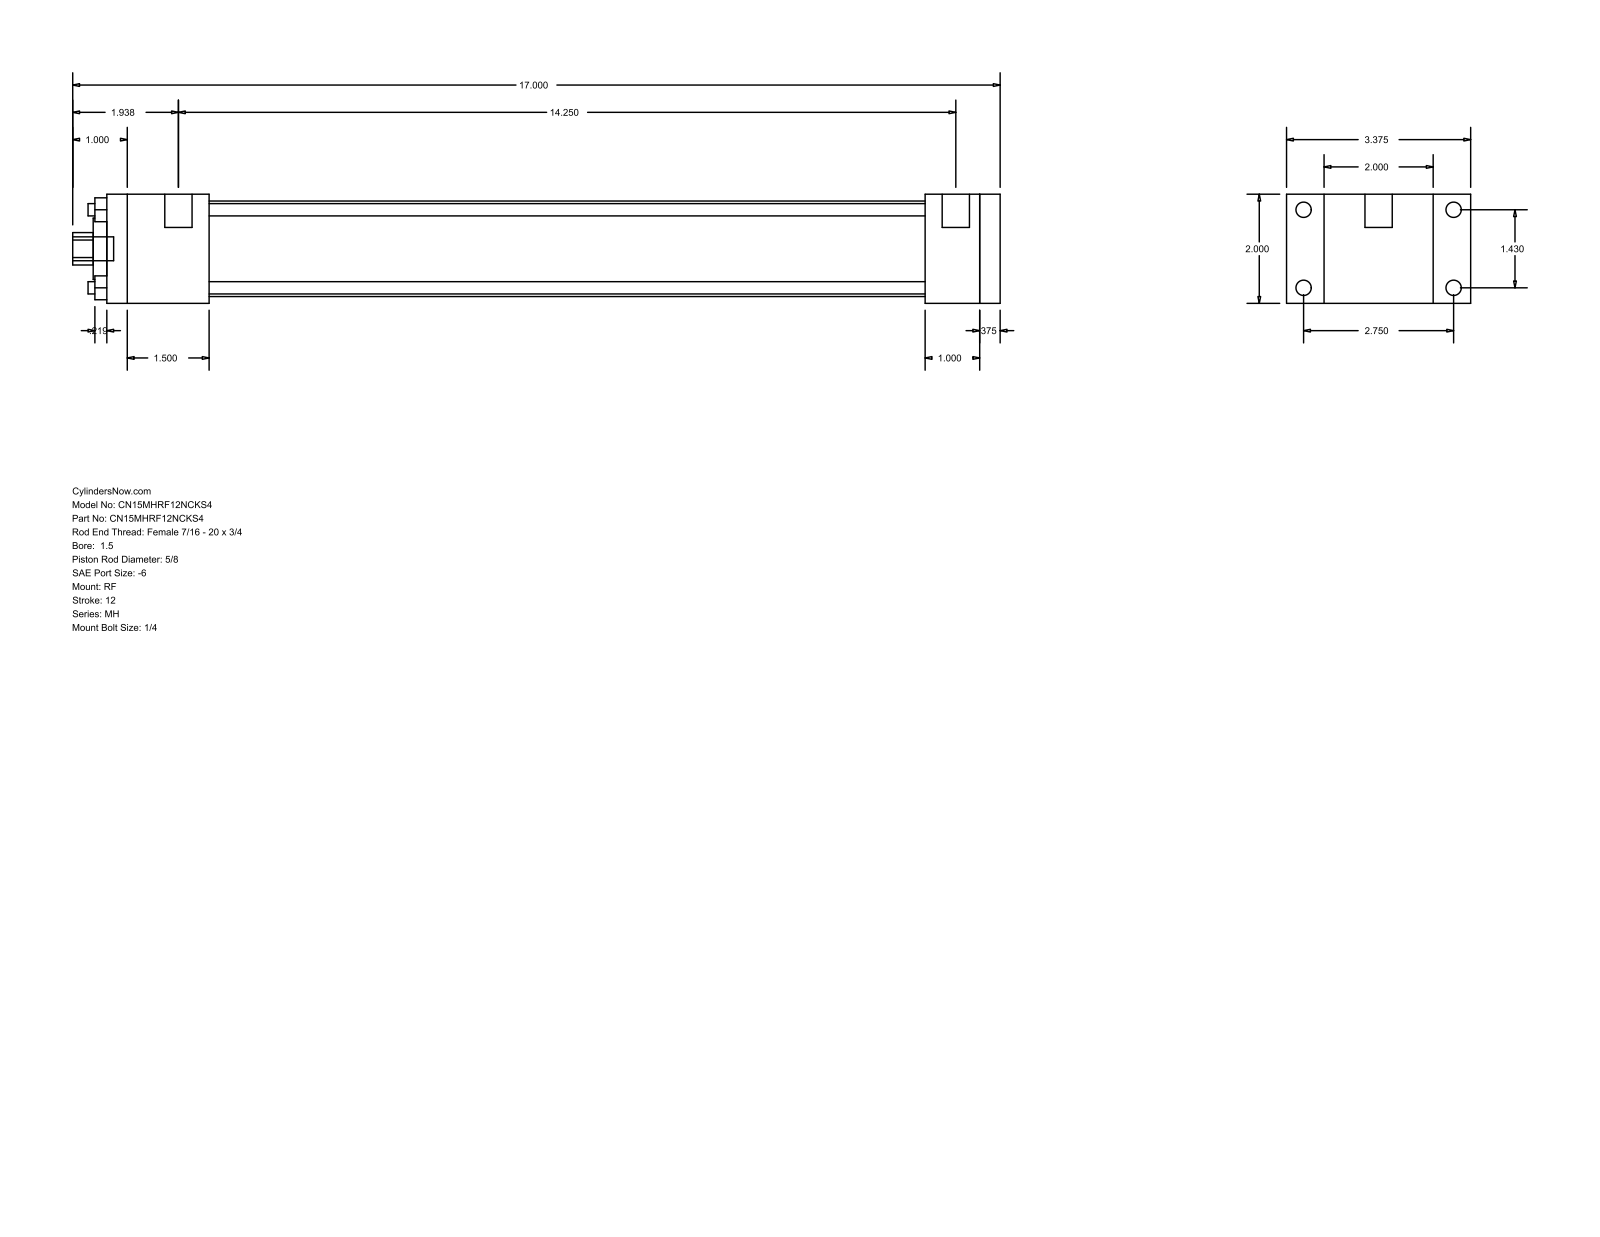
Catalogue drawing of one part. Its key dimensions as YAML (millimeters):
part_name: "MH_RF__0150_0.625"
step_written_by: "GSSL Pune (CONFIG_CONTROL_DESIGN)"
units: millimeters
bodies: {solids: 0, faces: 92, planar: 64, cylindrical: 28, other: 0}
overall_size: [431.8, 85.72, 50.8]
round_holes:
  - {diameter: 5.71, count: 4}
  - {diameter: 15.88, count: 1}
  - {diameter: 28.57, count: 1}
  - {diameter: 44.45, count: 1}
round_bosses_or_shafts:
  - {diameter: 7.14, count: 4}
  - {diameter: 5.56, count: 4}
  - {diameter: 12.7, count: 2}
  - {diameter: 11.11, count: 1}
partial_cylinders:
  - {radius: 7.54, count: 1}
face_to_face_distances: [50.8, 9.53, 415.92, 406.39, 17.46, 68.26, 381, 25.39, 34.92, 47.62]
hole_center_spacings: [25.68, 36.32, 51.36]
